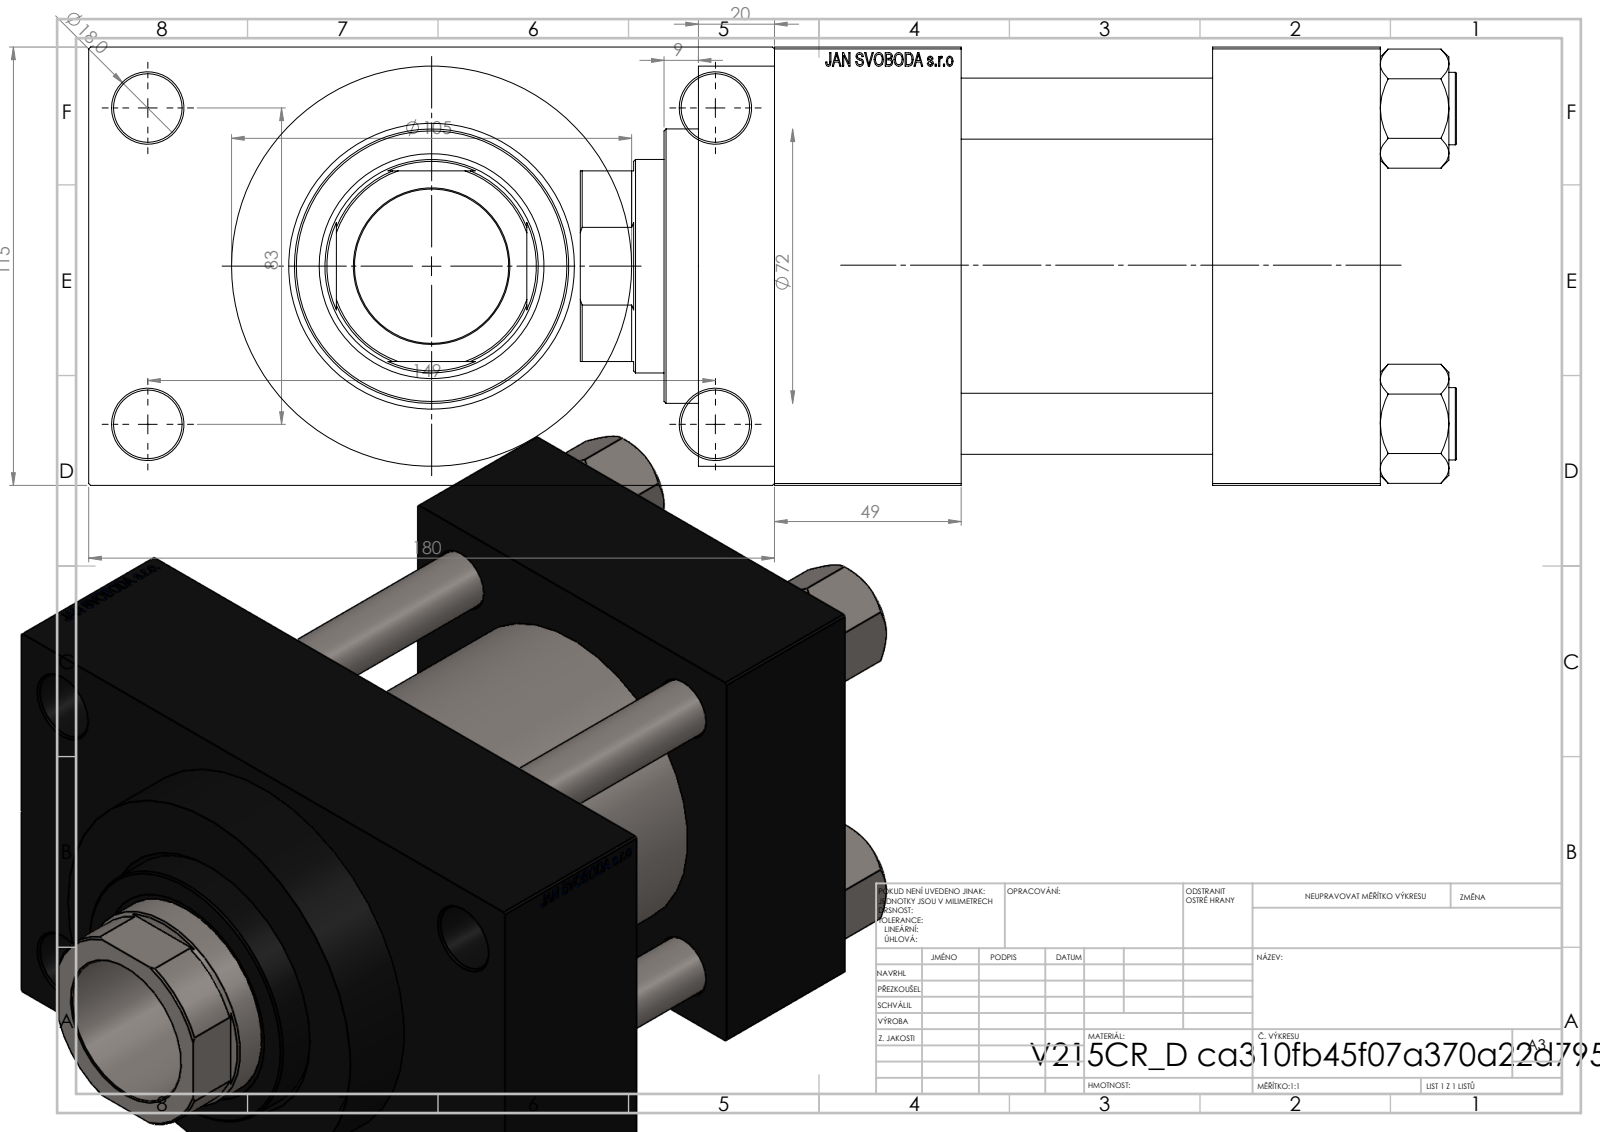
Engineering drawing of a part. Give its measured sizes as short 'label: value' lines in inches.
name: V215CR_D_Body; NUT_M5_D; V215CR_VCP_D; V215_VC_A (+1 more)
written by: SolidWorks 2019 (CONFIG_CONTROL_DESIGN)
unit: in
bodies: 11 solids, 1150 faces (544 planar, 86 cylindrical, 520 other)
size: 9.055 × 7.087 × 4.528
volume: 128.2 in³; area: 481.3 in²
holes: 4× ⌀0.63, 4× ⌀0.709, 2× ⌀0.276, 2× ⌀1.041, 2× ⌀1.378, 1× ⌀1.594, 1× ⌀2.205, 1× ⌀2.323, 1× ⌀2.402, 1× ⌀2.835, 1× ⌀3.15
bosses: 4× ⌀0.748, 1× ⌀4.134, 1× ⌀3.386
rounds: 1× R1.063
face distances: 4.528, 2.598, 4.331, 1.732, 6.26, 1.929, 1.28, 5.807, 0.787, 2.717
hole spacings: 1.305, 2.302, 3.256, 3.357, 3.513, 4.561, 5.607, 3.268
